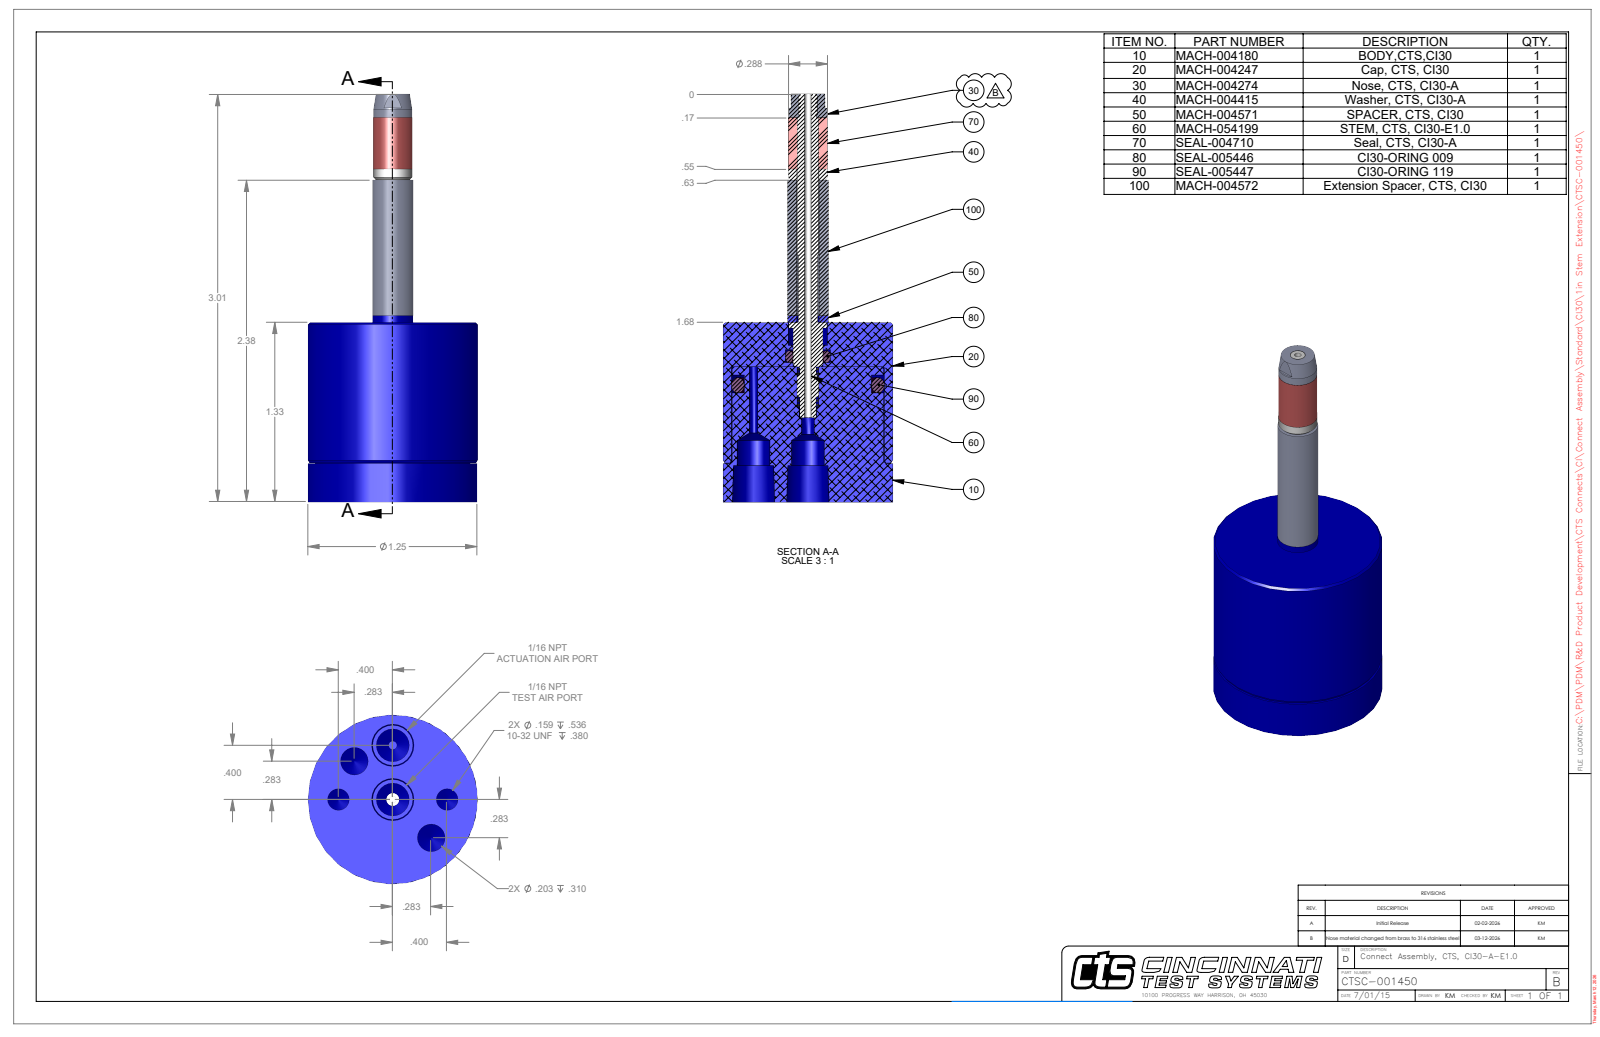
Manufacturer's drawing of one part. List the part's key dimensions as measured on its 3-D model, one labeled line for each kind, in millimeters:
Part name (STEP PRODUCT): CTSC-001450
STEP written by: SolidWorks 2023 (AUTOMOTIVE_DESIGN)
Units: millimetres
Bodies: 6 solids, 77 faces (33 planar, 27 cylindrical, 17 other)
Overall size (bounding box): 76.43 × 31.75 × 31.75
Volume: 26 578 mm³ · Surface area: 9 903 mm²
Round holes (diameter × count): ⌀4.04 ×2, ⌀5.16 ×2, ⌀6.15 ×2, ⌀1.32 ×1, ⌀1.57 ×1, ⌀2.38 ×1, ⌀2.87 ×1, ⌀3.94 ×1, ⌀4.18 ×1, ⌀7.34 ×1, ⌀28.58 ×1
Round bosses / shafts (diameter × count): ⌀31.75 ×1, ⌀28.32 ×1, ⌀7.62 ×1, ⌀7.32 ×1, ⌀7.24 ×1, ⌀7.04 ×1, ⌀3.94 ×1, ⌀3.51 ×1
Main face-to-face distances: 33.66, 7.28, 26.38, 7.37, 26.29, 72.01, 64.73, 64.64, 38.35, 34.93
Hole centre spacings: 7.77, 10.16, 18.77, 10.15, 14.37, 20.31, 20.32
